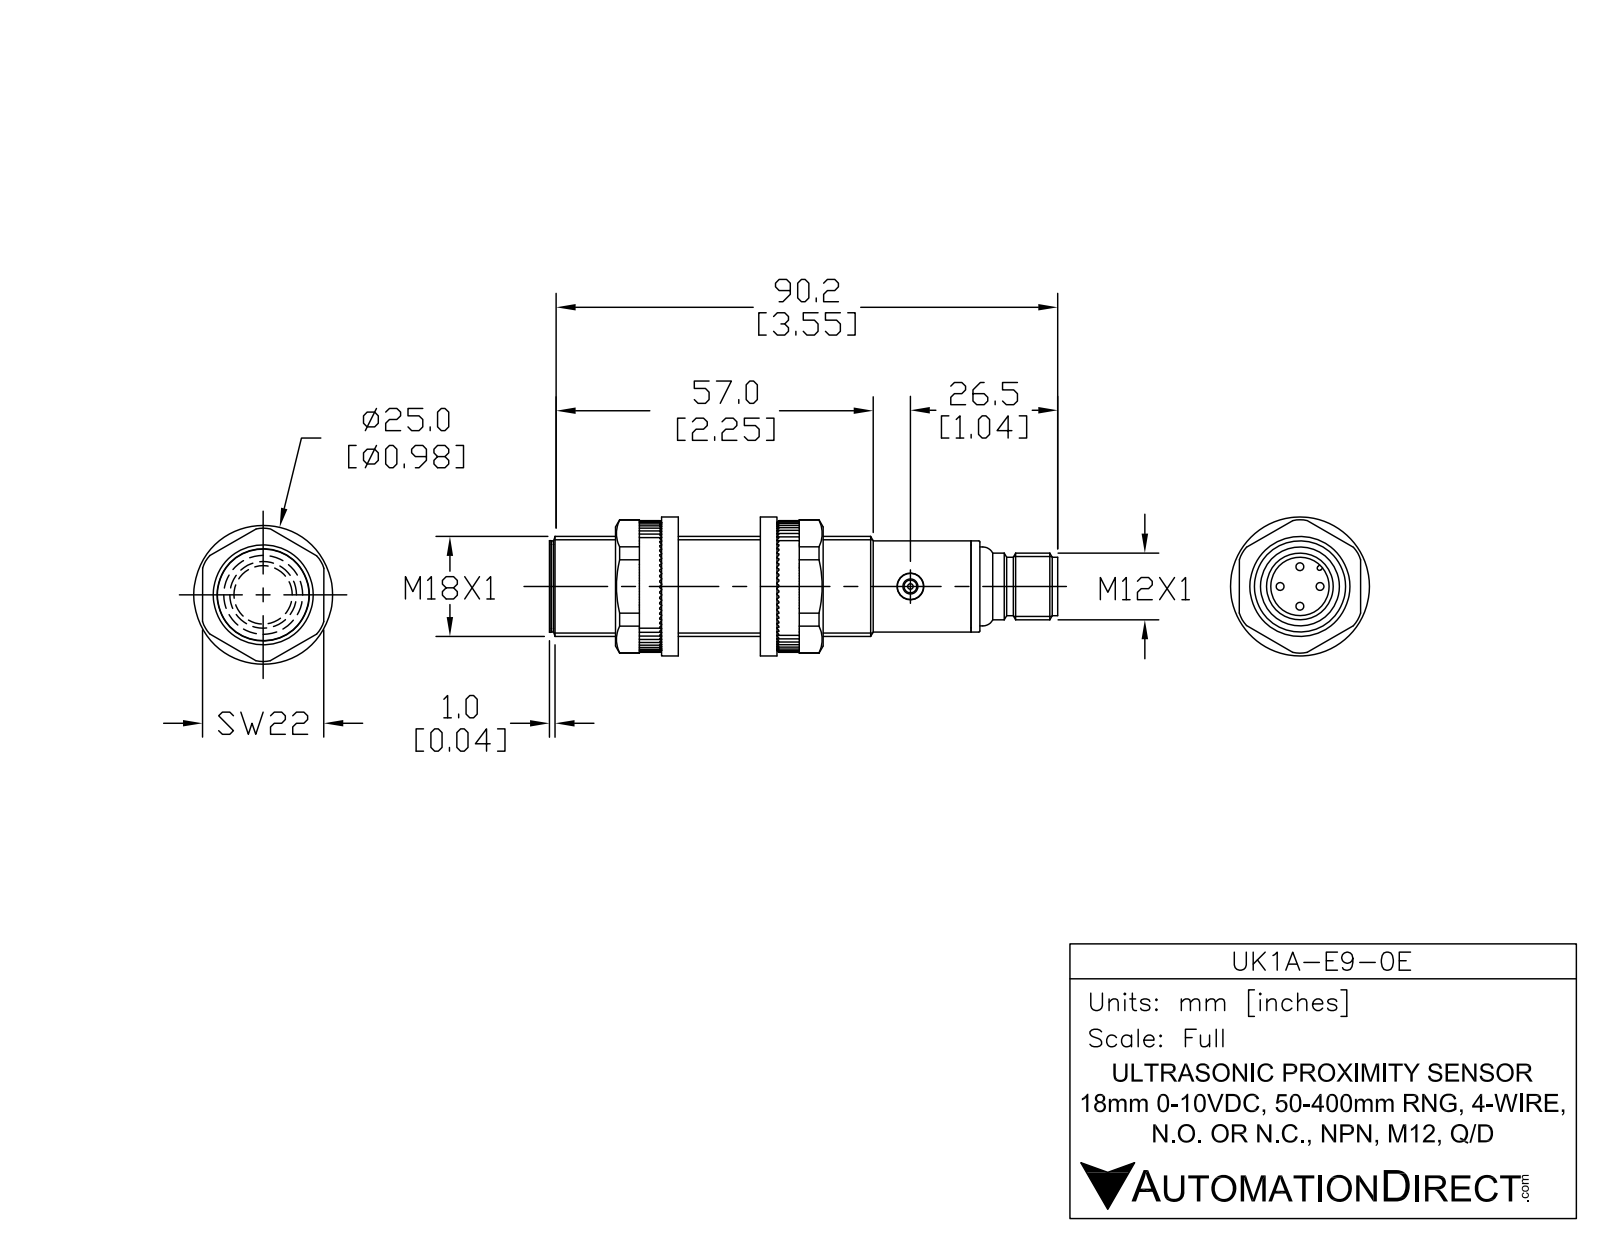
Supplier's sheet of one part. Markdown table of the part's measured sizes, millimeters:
| quantity | value |
| --- | --- |
| part name | UK1A-E9-0E |
| STEP written by | SolidWorks 2017 (AUTOMOTIVE_DESIGN) |
| units | millimeters |
| bodies | 6 solids, 106 faces (21 planar, 48 cylindrical, 37 other) |
| overall size | 91.6 × 18 × 18 |
| volume | 19 700 mm³ |
| surface area | 6 890 mm² |
| round holes (diameter × count) | 2.7 × 1, 4.7 × 1, 7 × 1, 8.3 × 1, 9.5 × 1 |
| round bosses / shafts (diameter × count) | 1 × 4, 18 × 1, 16.6 × 1, 16.4 × 1, 15.8 × 1, 14.2 × 1, 12 × 1, 10.5 × 1 |
| partial cylindrical surfaces (radius × count) | 0.6 × 1 |
| main face-to-face distances | 75.1, 1, 76.1, 0.9, 76, 1.1, 4, 77.6, 77.5, 76.6 |
